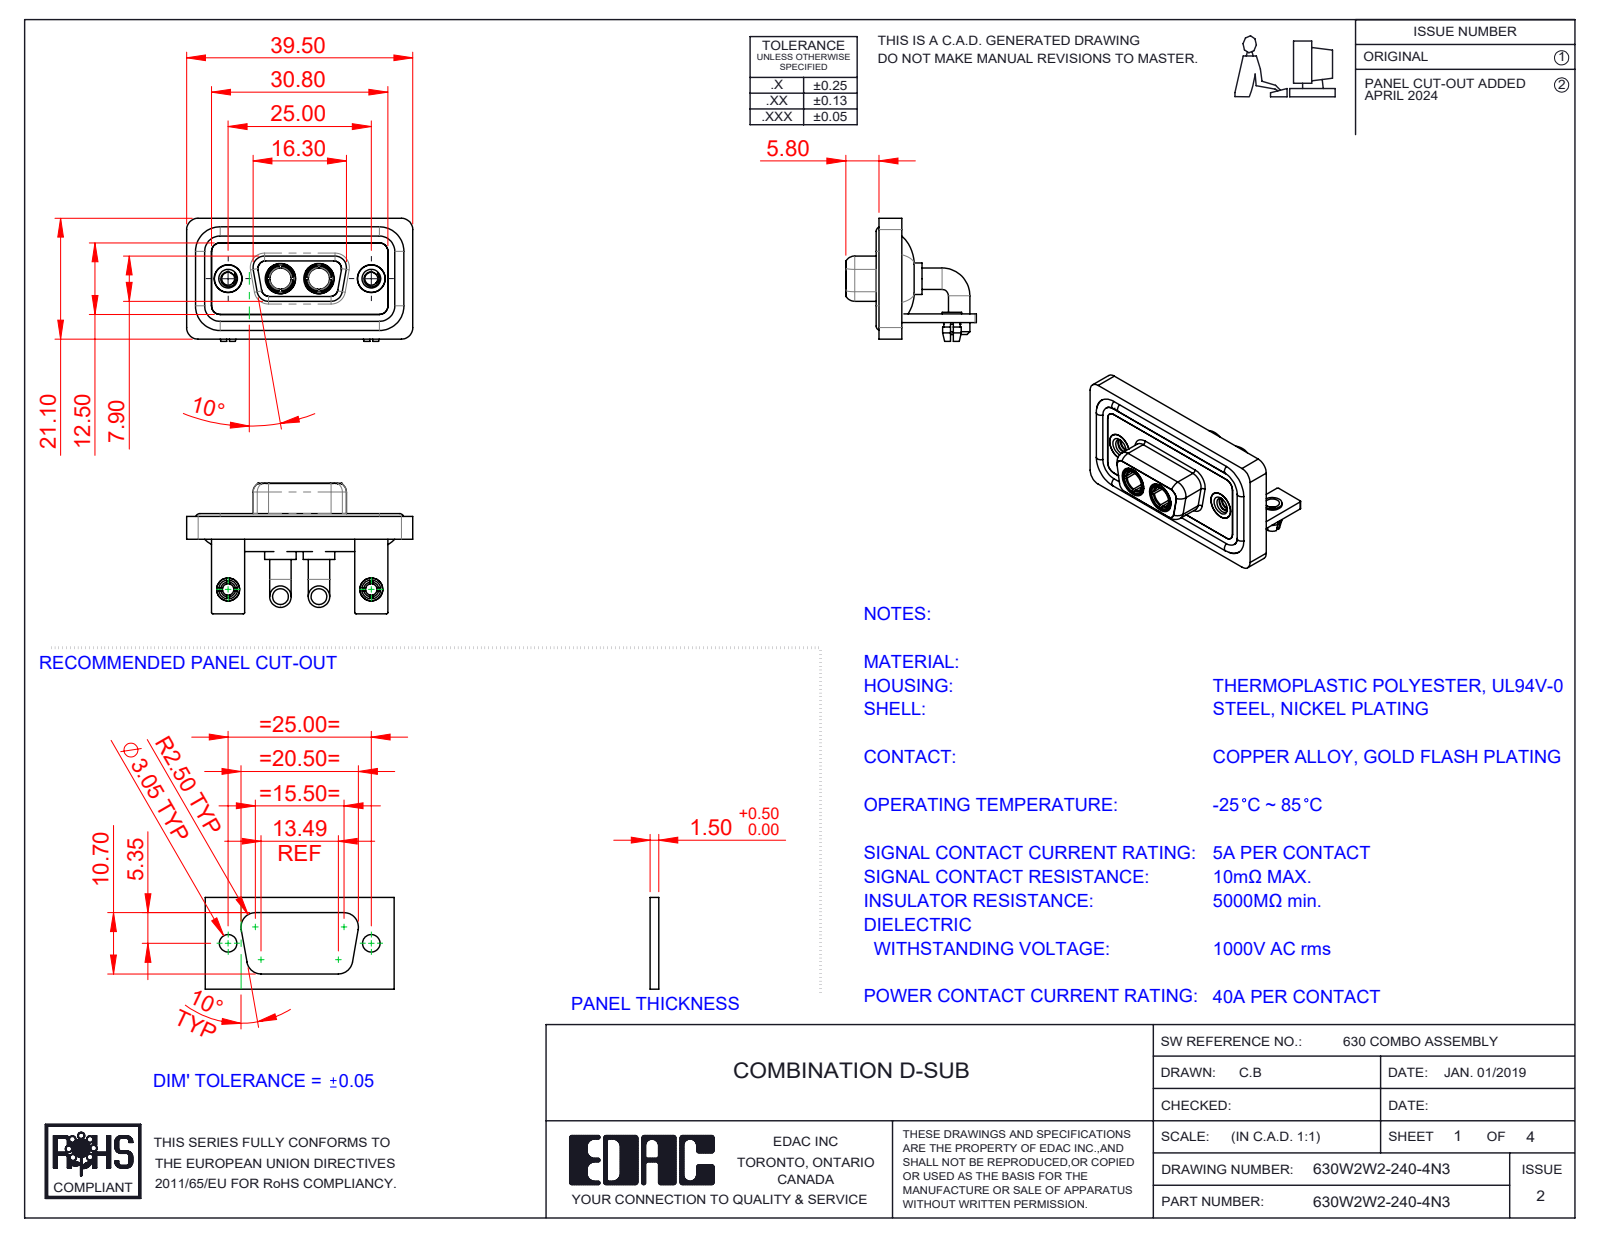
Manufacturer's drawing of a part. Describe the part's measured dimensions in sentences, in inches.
The part is named "630Combo Waterproof Housing_09 Contacts; 630Combo Threaded Rivet_2; Power Socket_40A RA; 630Combo Shell Front_09 Contacts (+5 more)". Its 3-D file was written by "SolidWorks 2023 (CONFIG_CONTROL_DESIGN)". It is 15 solids with 682 faces: 231 planar, 294 cylindrical and 157 other. Overall it measures 1.555 by 0.898 by 0.846 inches. Its volume is 0.327 cubic inches and its surface area 13.67 square inches. Round holes: 4 of diameter 0.191, 2 of diameter 0.079, 2 of diameter 0.089, 2 of diameter 0.098, 2 of diameter 0.126, 2 of diameter 0.146, 2 of diameter 0.157, 2 of diameter 0.159, 2 of diameter 0.197, 2 of diameter 0.209. Round bosses or shafts: 4 of diameter 0.148, 4 of diameter 0.063, 2 of diameter 0.217, 2 of diameter 0.205, 2 of diameter 0.195, 2 of diameter 0.195, 2 of diameter 0.189, 2 of diameter 0.187. Partial cylindrical surfaces (rounded edges, fillets, slot ends): 19 of radius 0.079, 18 of radius 0.059, 16 of radius 0.01, 8 of radius 0.053, 8 of radius 0.063, 5 of radius 0.02, 4 of radius 0.024, 4 of radius 0.026. The main face-to-face distances are 0.016, 0.114, 0.059, 0.071, 0.043, 0.146, 0.031, 0.098, 0.063, 0.122. The hole center spacings are 0.36, 0.624, 0.984, 0.265.
